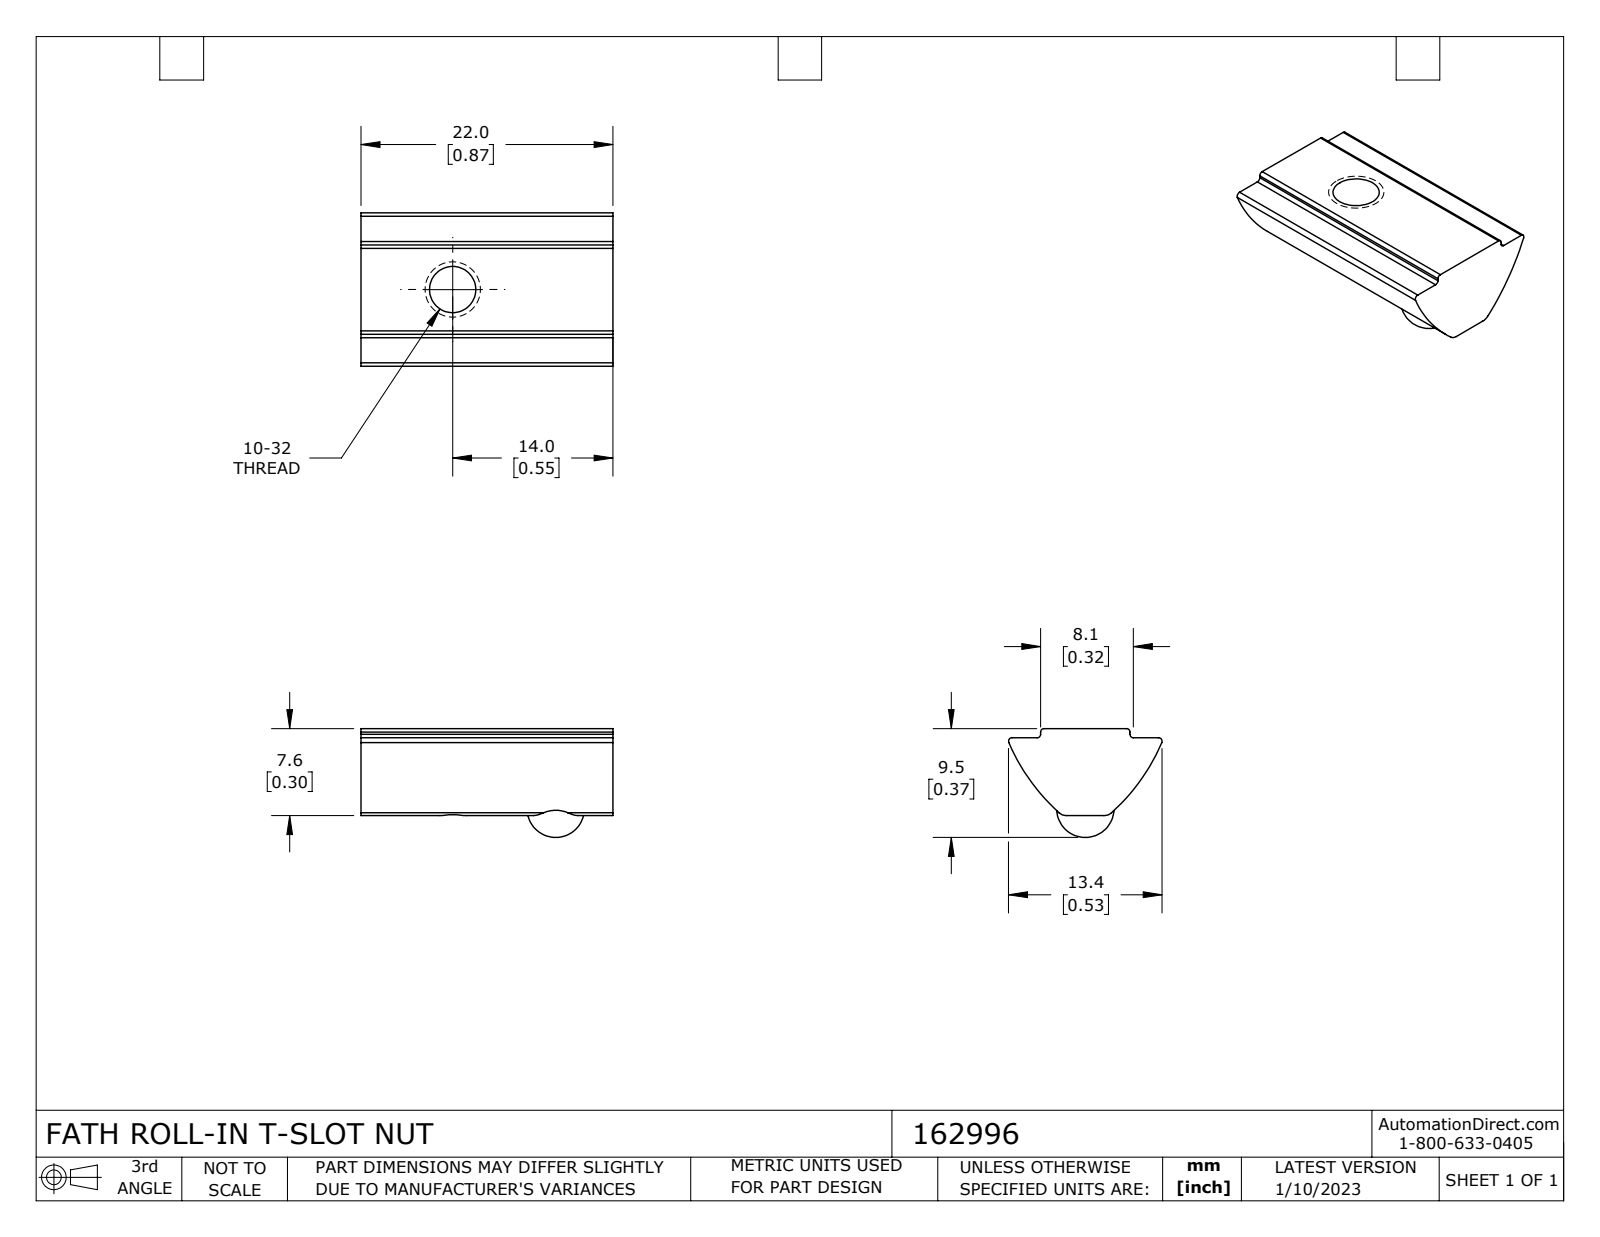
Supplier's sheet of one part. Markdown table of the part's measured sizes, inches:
| quantity | value |
| --- | --- |
| part name | 162996 |
| STEP written by | SolidWorks 2021 (CONFIG_CONTROL_DESIGN) |
| units | inches |
| bodies | 2 solids, 31 faces (10 planar, 17 cylindrical, 4 other) |
| overall size | 0.866 × 0.528 × 0.374 |
| volume | 0.087 in³ |
| surface area | 1.792 in² |
| round holes (diameter × count) | 0.159 × 1, 0.199 × 1 |
| partial cylindrical surfaces (radius × count) | 0.012 × 6, 0.039 × 2, 0.689 × 2 |
| main face-to-face distances | 0.031, 0.866, 0.268, 0.299, 0.307 |
| hole center spacings | 0.354 |
